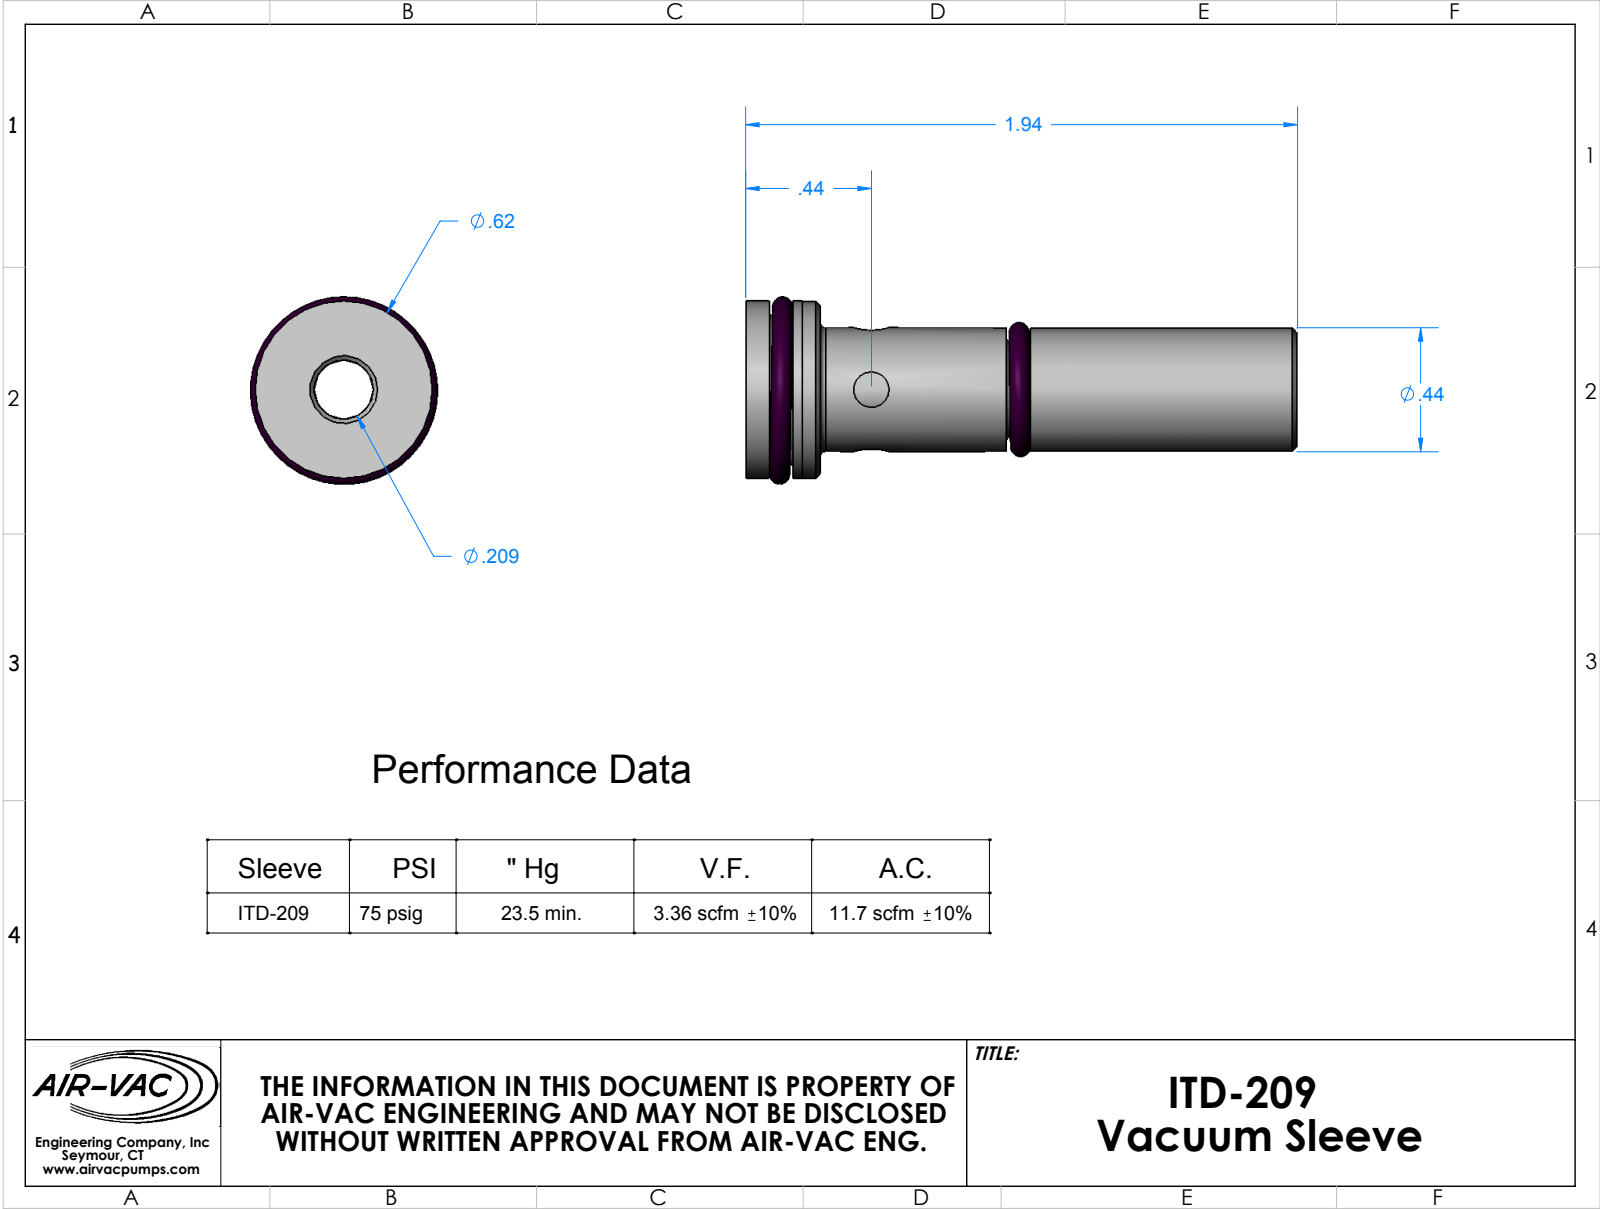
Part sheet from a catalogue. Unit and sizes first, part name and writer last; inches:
Units: inches
Overall size (bounding box): 1.94 × 0.659 × 0.659
Round holes (diameter × count): ⌀0.125 ×2, ⌀0.209 ×1, ⌀0.301 ×1
Round bosses / shafts (diameter × count): ⌀0.624 ×1, ⌀0.519 ×1, ⌀0.436 ×1, ⌀0.332 ×1, ⌀0.301 ×1, ⌀0.293 ×1
Main face-to-face distances: 0.2, 0.085, 0.062, 0.262, 1.678, 1.74, 1.94, 0.836, 0.033, 0.095
Volume: 0.259 in³ · Surface area: 6.806 in²
Bodies: 4 solids, 72 faces (12 planar, 32 cylindrical, 28 other)
Part name (STEP PRODUCT): ITD-209; ITD-209E_Web Model; ITD-209G_Web Model; 2-14-BUNA 70_VS260GOR (+1 more)
STEP written by: SolidWorks 2008 (AUTOMOTIVE_DESIGN)
